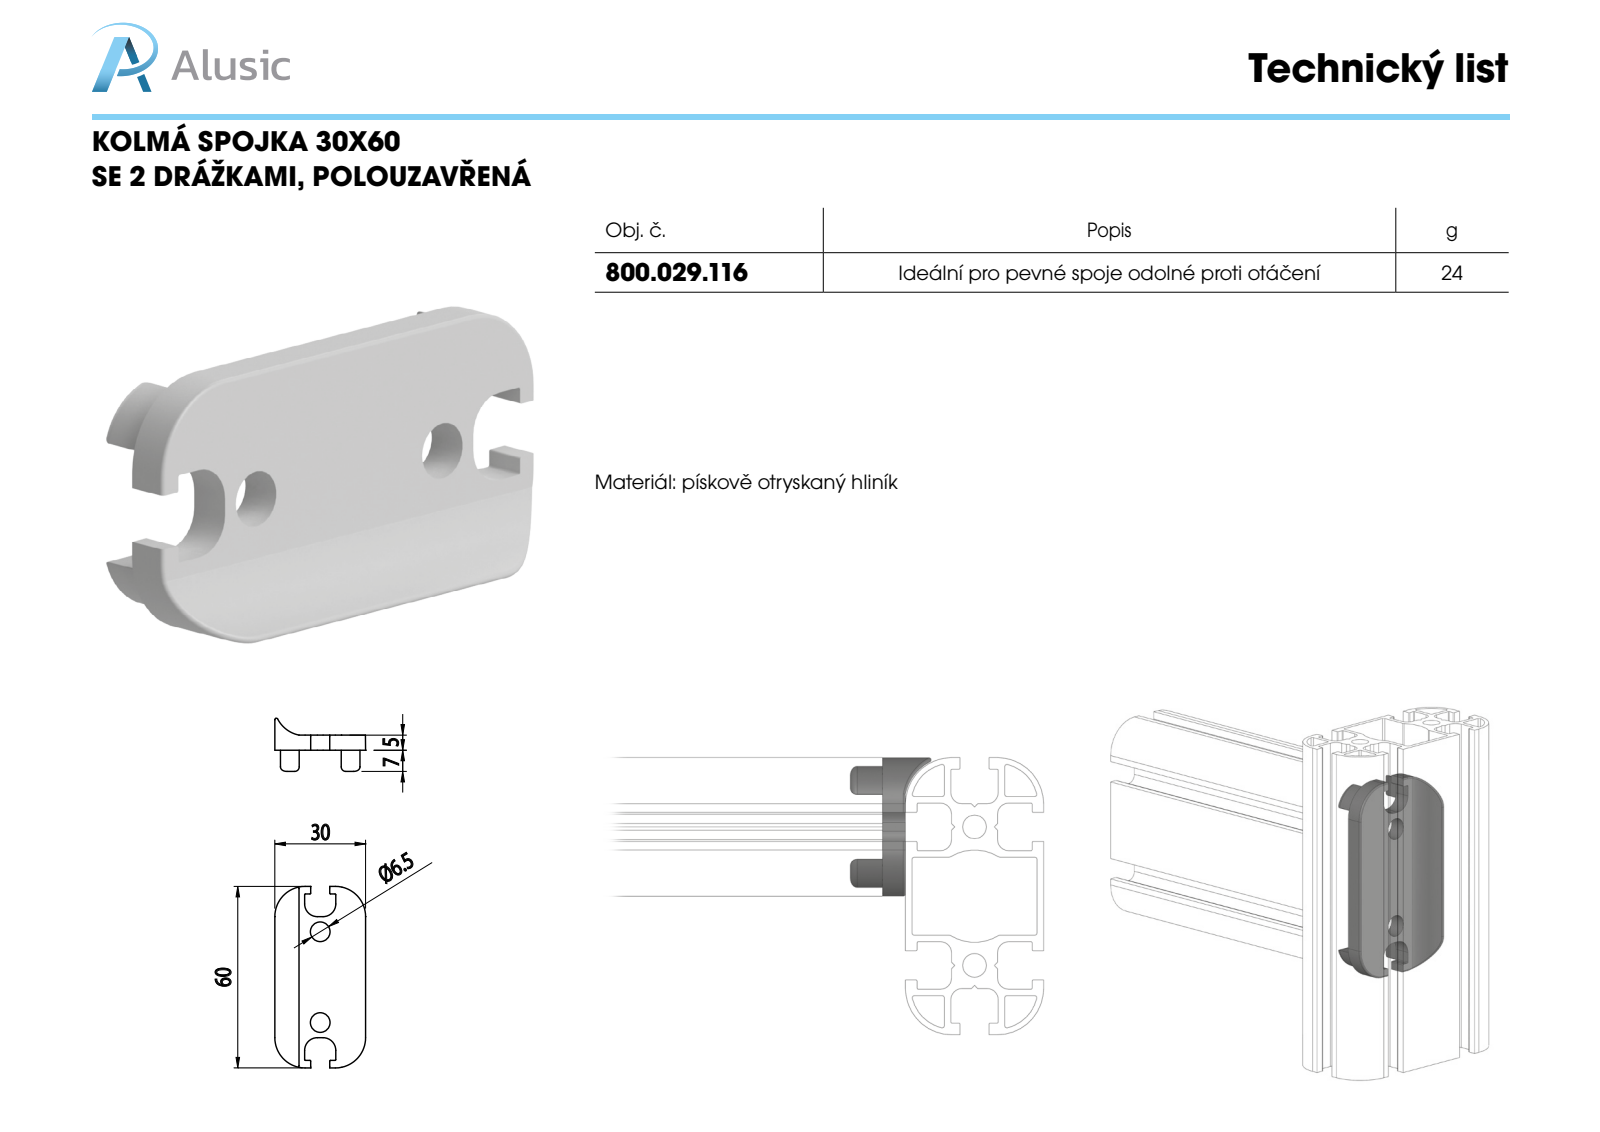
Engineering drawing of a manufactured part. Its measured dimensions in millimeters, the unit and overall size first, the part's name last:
Units: millimetres
Overall size (bounding box): 60 × 30 × 17.58
Round holes (diameter × count): ⌀6.5 ×2
Partial cylindrical surfaces — rounded edges, fillets, slot ends (radius × count): R0.1 ×12, R0.25 ×8, R0.5 ×4, R1.5 ×4, R4.2 ×4, R8.4 ×4, R10 ×4, R10.2 ×1
Main face-to-face distances: 5, 30, 8.05, 21.95, 13.9, 43.9, 9.85, 20.15, 1.8, 12.1
Hole centre spacings: 30
Volume: 9 004 mm³ · Surface area: 5 132 mm²
Bodies: 1 solid, 109 faces (34 planar, 53 cylindrical, 22 other)
Part name (STEP PRODUCT): 800.029.116
STEP written by: SolidWorks 2012 (CONFIG_CONTROL_DESIGN)
